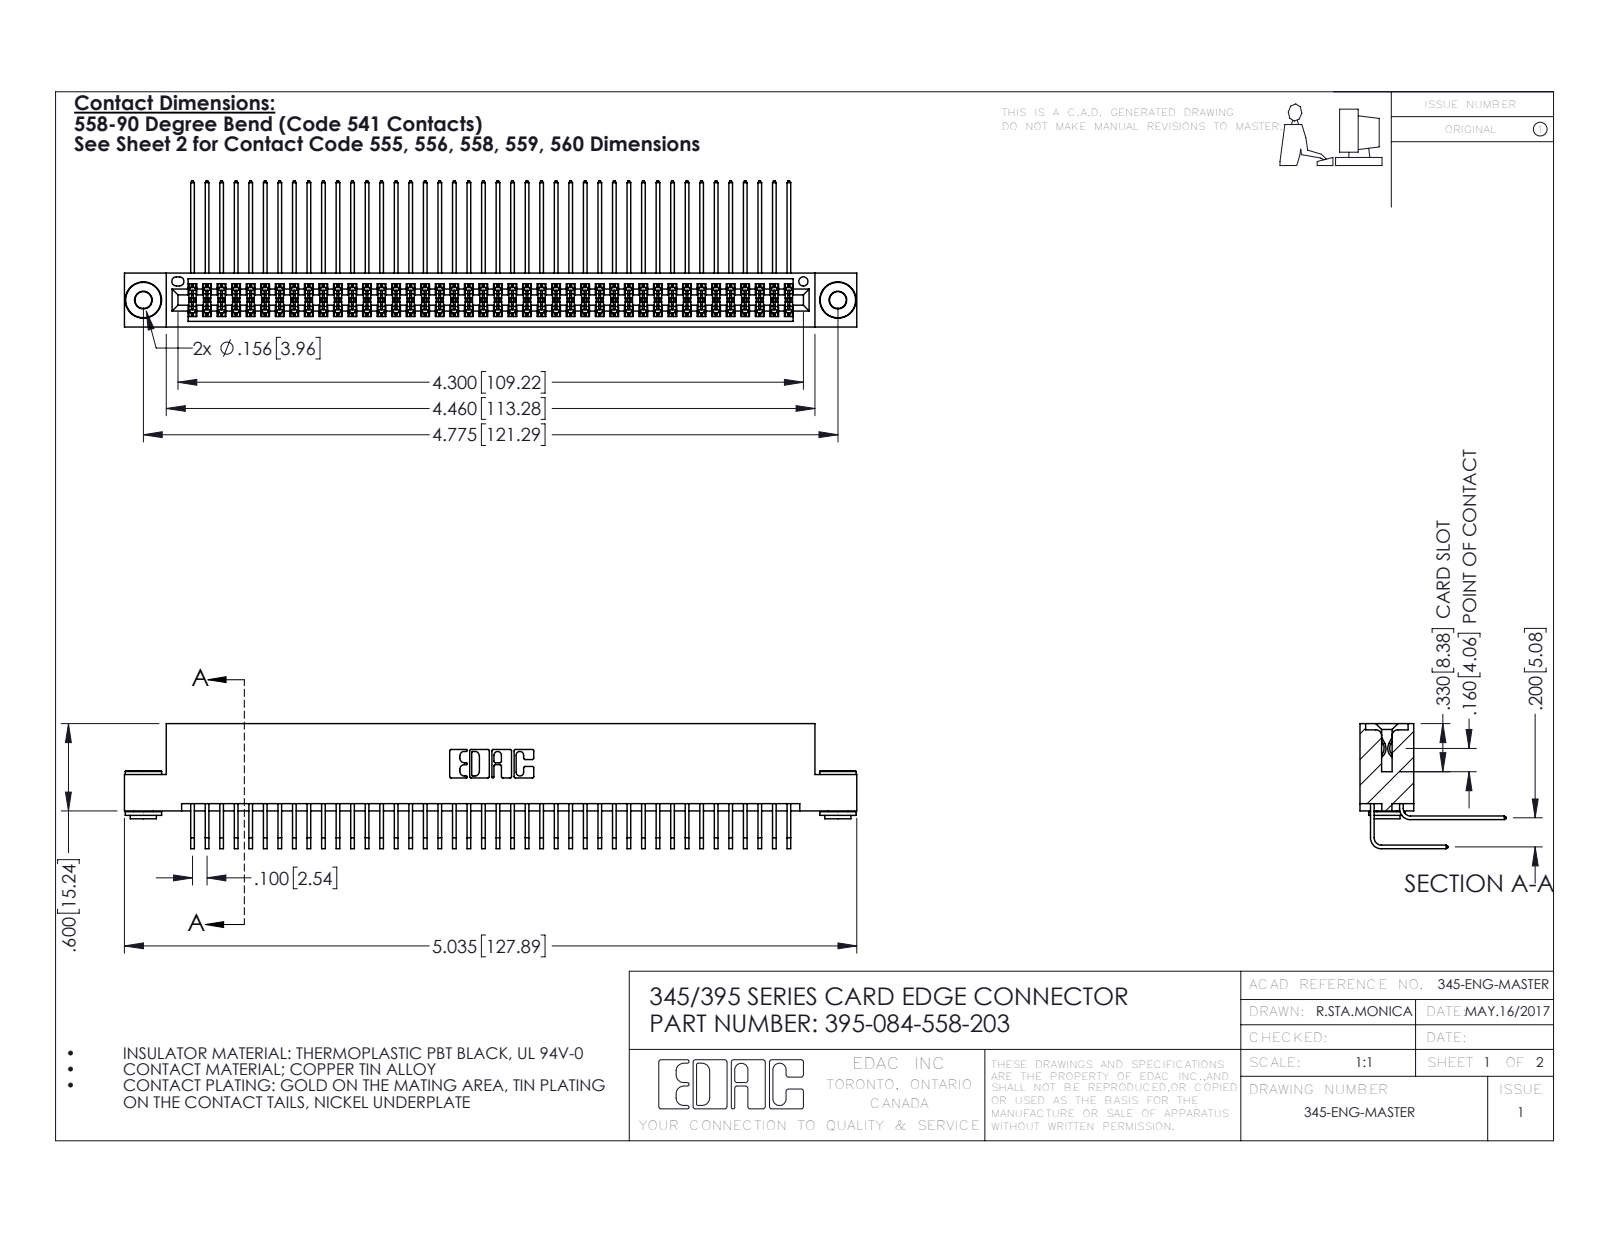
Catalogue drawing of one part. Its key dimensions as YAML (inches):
part_name: "395-084-558-203; 345-292-001_558 559 Tail - 1; 345-250-002_345-250-002-102; 345-292-001_558 Tail - 2 (+1 more)"
step_written_by: "SolidWorks 2016 (CONFIG_CONTROL_DESIGN)"
units: inches
bodies: {solids: 87, faces: 4532, planar: 3030, cylindrical: 1494, other: 8}
overall_size: [5.035, 1.005, 0.859]
volume: 0.789
surface_area: 33.47
round_holes:
  - {diameter: 0.116, count: 2}
  - {diameter: 0.156, count: 2}
  - {diameter: 0.064, count: 1}
round_bosses_or_shafts:
  - {diameter: 0.25, count: 2}
  - {diameter: 0.18, count: 2}
  - {diameter: 0.136, count: 2}
partial_cylinders:
  - {radius: 0.006, count: 127}
  - {radius: 0.01, count: 22}
  - {radius: 0.007, count: 6}
  - {radius: 0.031, count: 6}
  - {radius: 0.026, count: 3}
  - {radius: 0.014, count: 2}
  - {radius: 0.019, count: 2}
  - {radius: 0.022, count: 2}
face_to_face_distances: [0.072, 0.298, 0.2, 0.37, 0.025, 0.098, 0.272, 0.225, 0.025, 0.285]
hole_center_spacings: [0.27, 4.539, 4.775]
